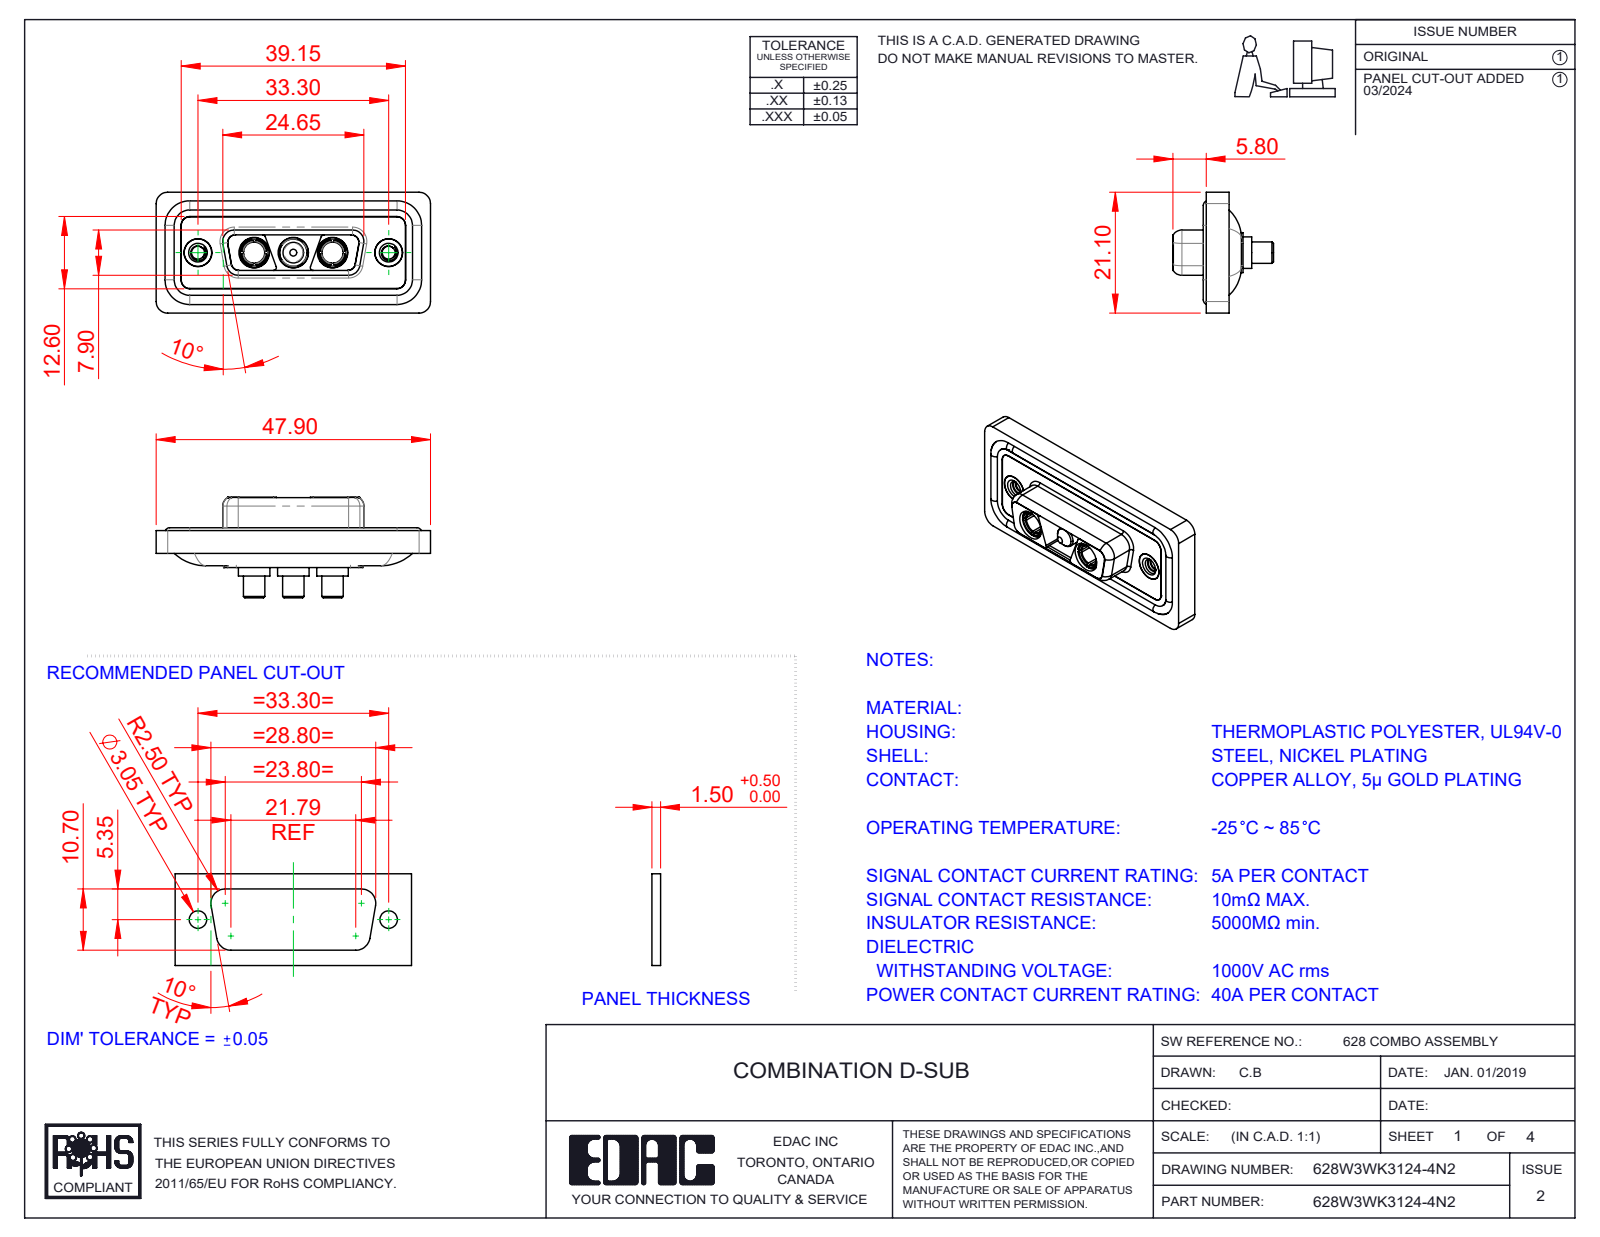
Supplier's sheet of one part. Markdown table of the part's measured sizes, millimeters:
| quantity | value |
| --- | --- |
| part name | 628Combo Housing_3WK3; Power Pin_40A S; 628Combo Shell Front_15 Contacts; 628Combo Shell Rear_15 Contacts (+4 more) |
| STEP written by | SolidWorks 2023 (CONFIG_CONTROL_DESIGN) |
| units | millimeters |
| bodies | 13 solids, 583 faces (178 planar, 258 cylindrical, 147 other) |
| overall size | 47.9 × 21.1 × 17.55 |
| volume | 5 933 mm³ |
| surface area | 9 537 mm² |
| round holes (diameter × count) | 4.85 × 5, 5.3 × 3, 2.26 × 2, 3.7 × 2, 4 × 2, 4.05 × 2, 5 × 2 |
| round bosses / shafts (diameter × count) | 1.6 × 4, 5.5 × 3, 5.2 × 3, 4.75 × 3, 3.75 × 3, 4.96 × 2, 4.95 × 2, 4.8 × 2 |
| partial cylindrical surfaces (radius × count) | 1.5 × 22, 2 × 20, 1.35 × 12, 0.5 × 8, 1.6 × 8, 0.25 × 4, 0.6 × 4, 0.65 × 4 |
| main face-to-face distances | 0.4, 1.6, 0.5, 1.8, 1.1, 2.9, 5.65, 7.05, 5.35, 1.5 |
| hole center spacings | 6.85, 9.8, 16.65, 23.5, 13.7, 33.3 |
